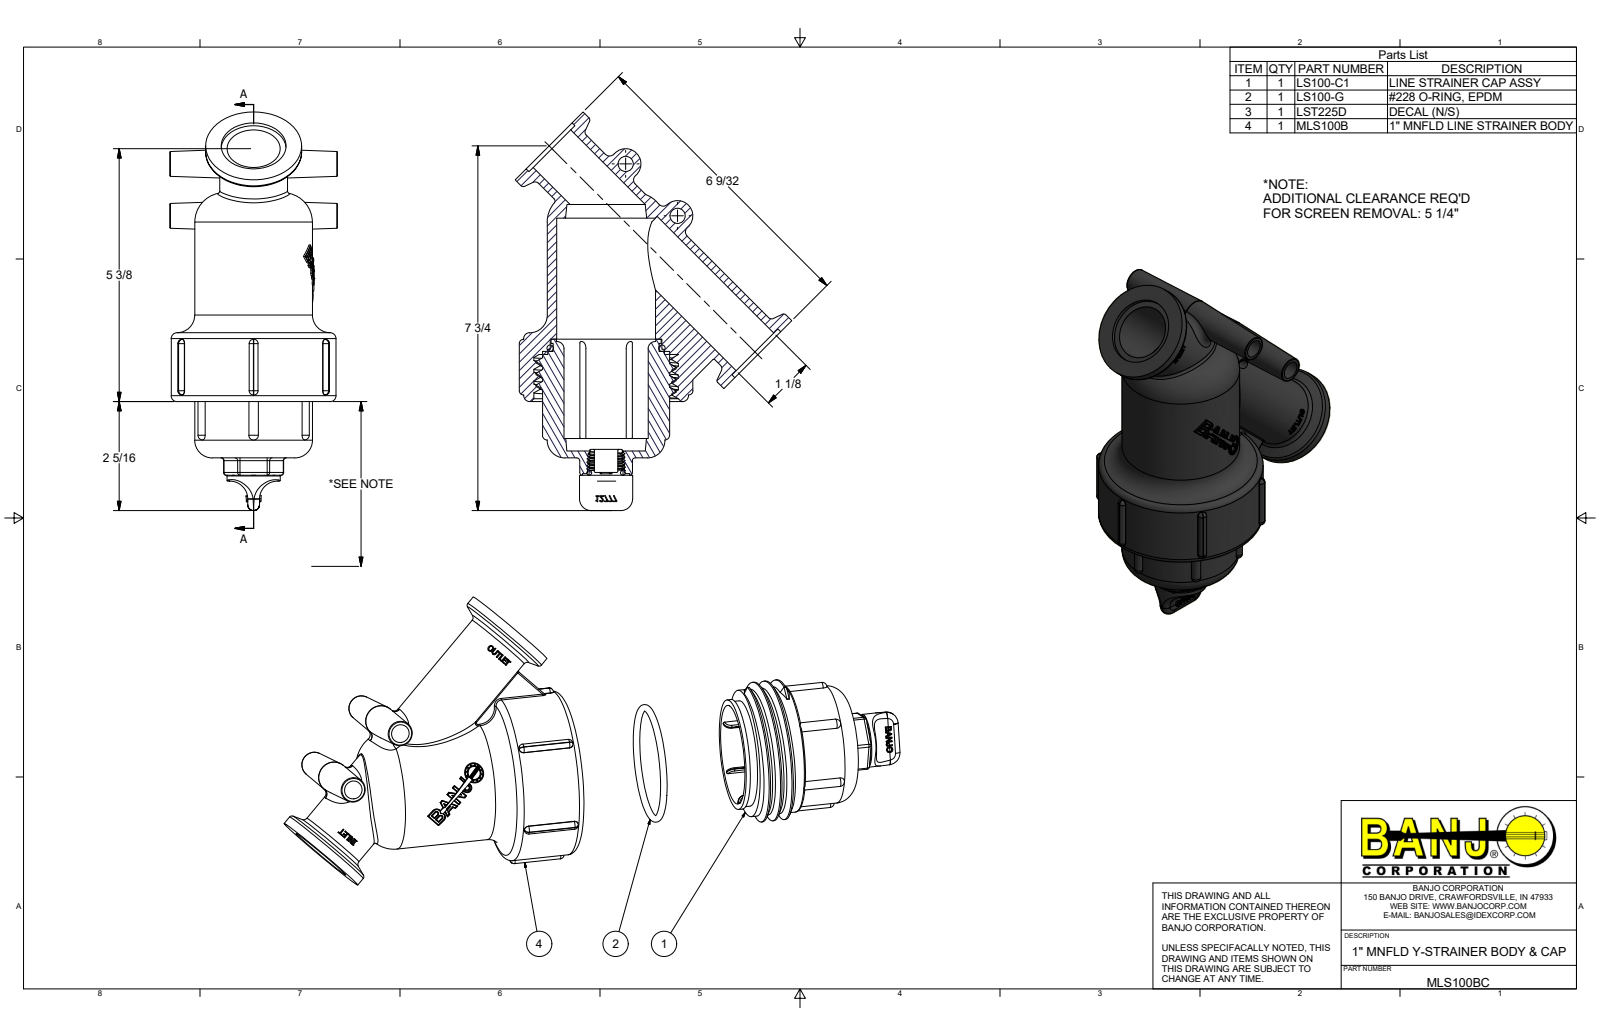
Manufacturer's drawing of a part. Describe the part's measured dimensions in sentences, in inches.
The part is named "MLS100B; LS100XC1; 12777; UV15163 (+3 more)". Its 3-D file was written by "Autodesk Inventor 2015 (AUTOMOTIVE_DESIGN)". It is 5 solids with 1073 faces: 552 planar, 238 cylindrical and 283 other. Overall it measures 8.465 by 5.876 by 3.563 inches. Its volume is 20.87 cubic inches and its surface area 213.4 square inches. Round holes: 2 of diameter 1.13, 2 of diameter 1.38, 1 of diameter 0.272, 1 of diameter 0.385, 1 of diameter 0.5, 1 of diameter 1.005, 1 of diameter 2.1, 1 of diameter 2.11, 1 of diameter 2.371, 1 of diameter 2.48, 1 of diameter 2.799, 1 of diameter 3.07. Round bosses or shafts: 2 of diameter 2.04, 1 of diameter 3.5, 1 of diameter 2.97, 1 of diameter 2.7, 1 of diameter 2.5, 1 of diameter 2.34, 1 of diameter 2.25, 1 of diameter 1.44. Partial cylindrical surfaces (rounded edges, fillets, slot ends): 39 of radius 0.09, 27 of radius 0.03, 18 of radius 0.06, 7 of radius 0.1, 6 of radius 0.15, 2 of radius 0.039, 2 of radius 0.049, 2 of radius 0.095. The main face-to-face distances are 0.065, 0.325, 2.05, 6.269, 2.375, 2.115, 0.26, 2.57, 2.83, 4.945.
